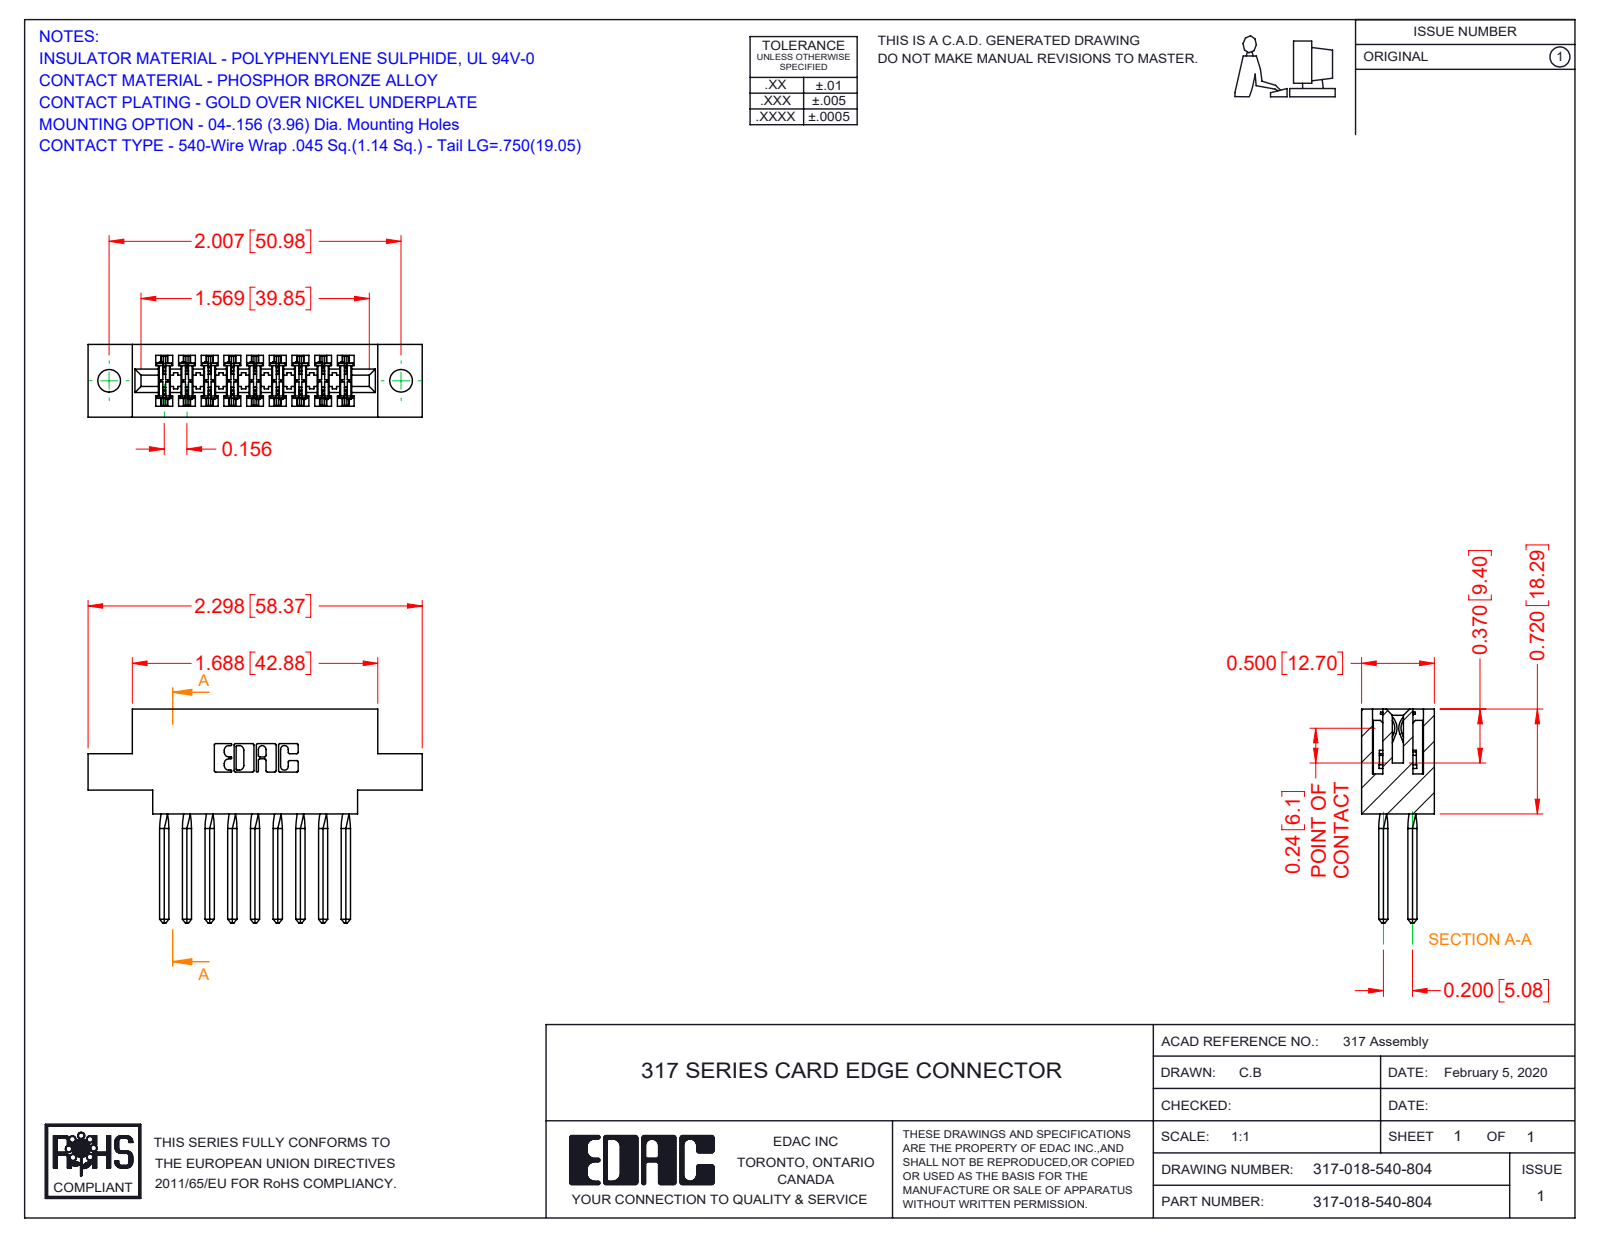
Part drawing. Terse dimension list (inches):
name: 317 Part_.156 Dia - TH; 317-018-540-804; 317-290-001_540
written by: SolidWorks 2016 (CONFIG_CONTROL_DESIGN)
unit: in
bodies: 19 solids, 1704 faces (1372 planar, 260 cylindrical, 72 other)
size: 2.298 × 1.47 × 0.5
volume: 0.524 in³; area: 17.65 in²
holes: 2× ⌀0.156
rounds: 36× R0.015, 22× R0.01, 6× R0.007, 6× R0.031, 3× R0.026, 2× R0.095, 2× R0.1, 2× R0.11
face distances: 0.5, 0.075, 0.425, 0.11, 0.22, 0.156, 0.35, 0.116, 0.331, 0.305
hole spacings: 2.007
